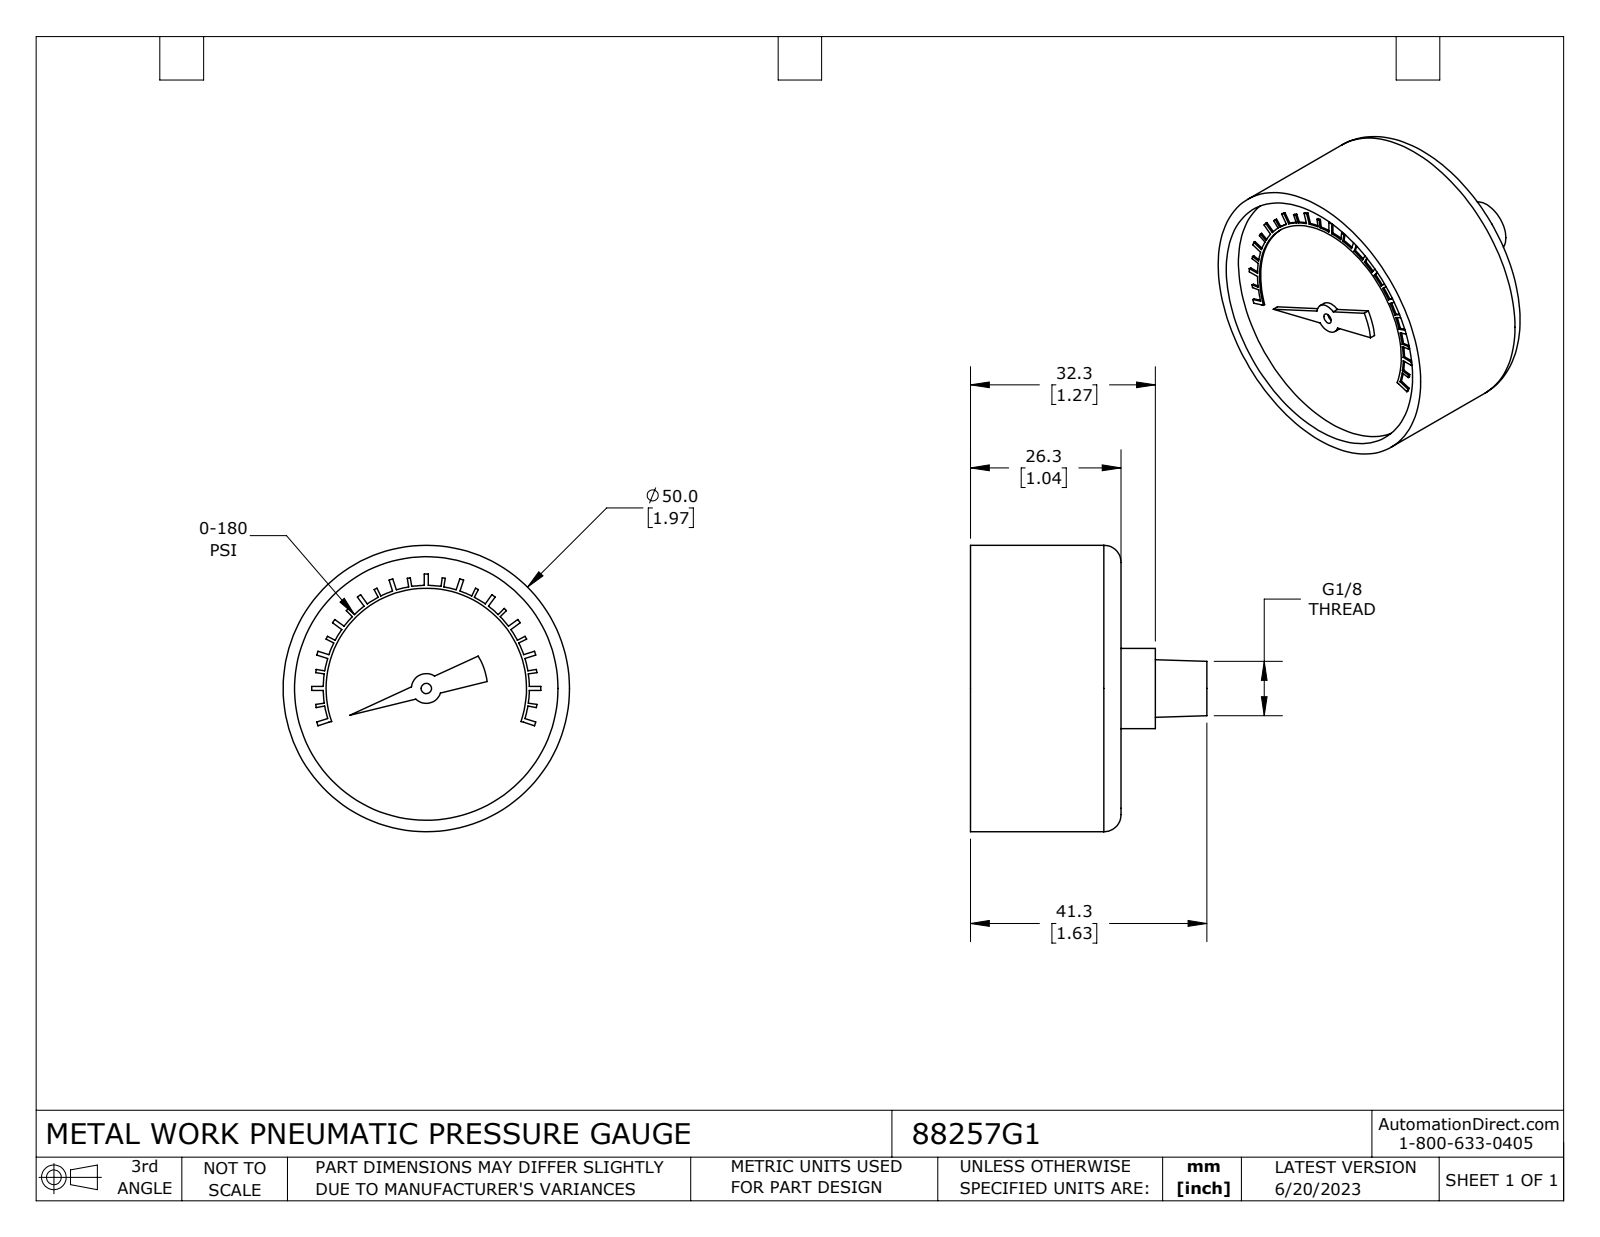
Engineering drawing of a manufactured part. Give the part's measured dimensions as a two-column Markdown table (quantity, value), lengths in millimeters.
| quantity | value |
| --- | --- |
| part name | 88257G1 |
| STEP written by | SolidWorks 2021 (CONFIG_CONTROL_DESIGN) |
| units | millimeters |
| bodies | 1 solid, 133 faces (93 planar, 36 cylindrical, 4 other) |
| overall size | 50 × 50 × 41.3 |
| volume | 48 340 mm³ |
| surface area | 9 026 mm² |
| round holes (diameter × count) | 1.8 × 1, 46 × 1 |
| round bosses / shafts (diameter × count) | 50 × 1 |
| partial cylindrical surfaces (radius × count) | 2.6 × 1, 10.7 × 1, 17.4 × 1, 17.4 × 1, 17.5 × 1, 17.5 × 1, 17.6 × 1, 18 × 1 |
| main face-to-face distances | 23.3, 26.3, 3, 14, 6, 29.3, 32.3, 9, 15, 38.3 |
